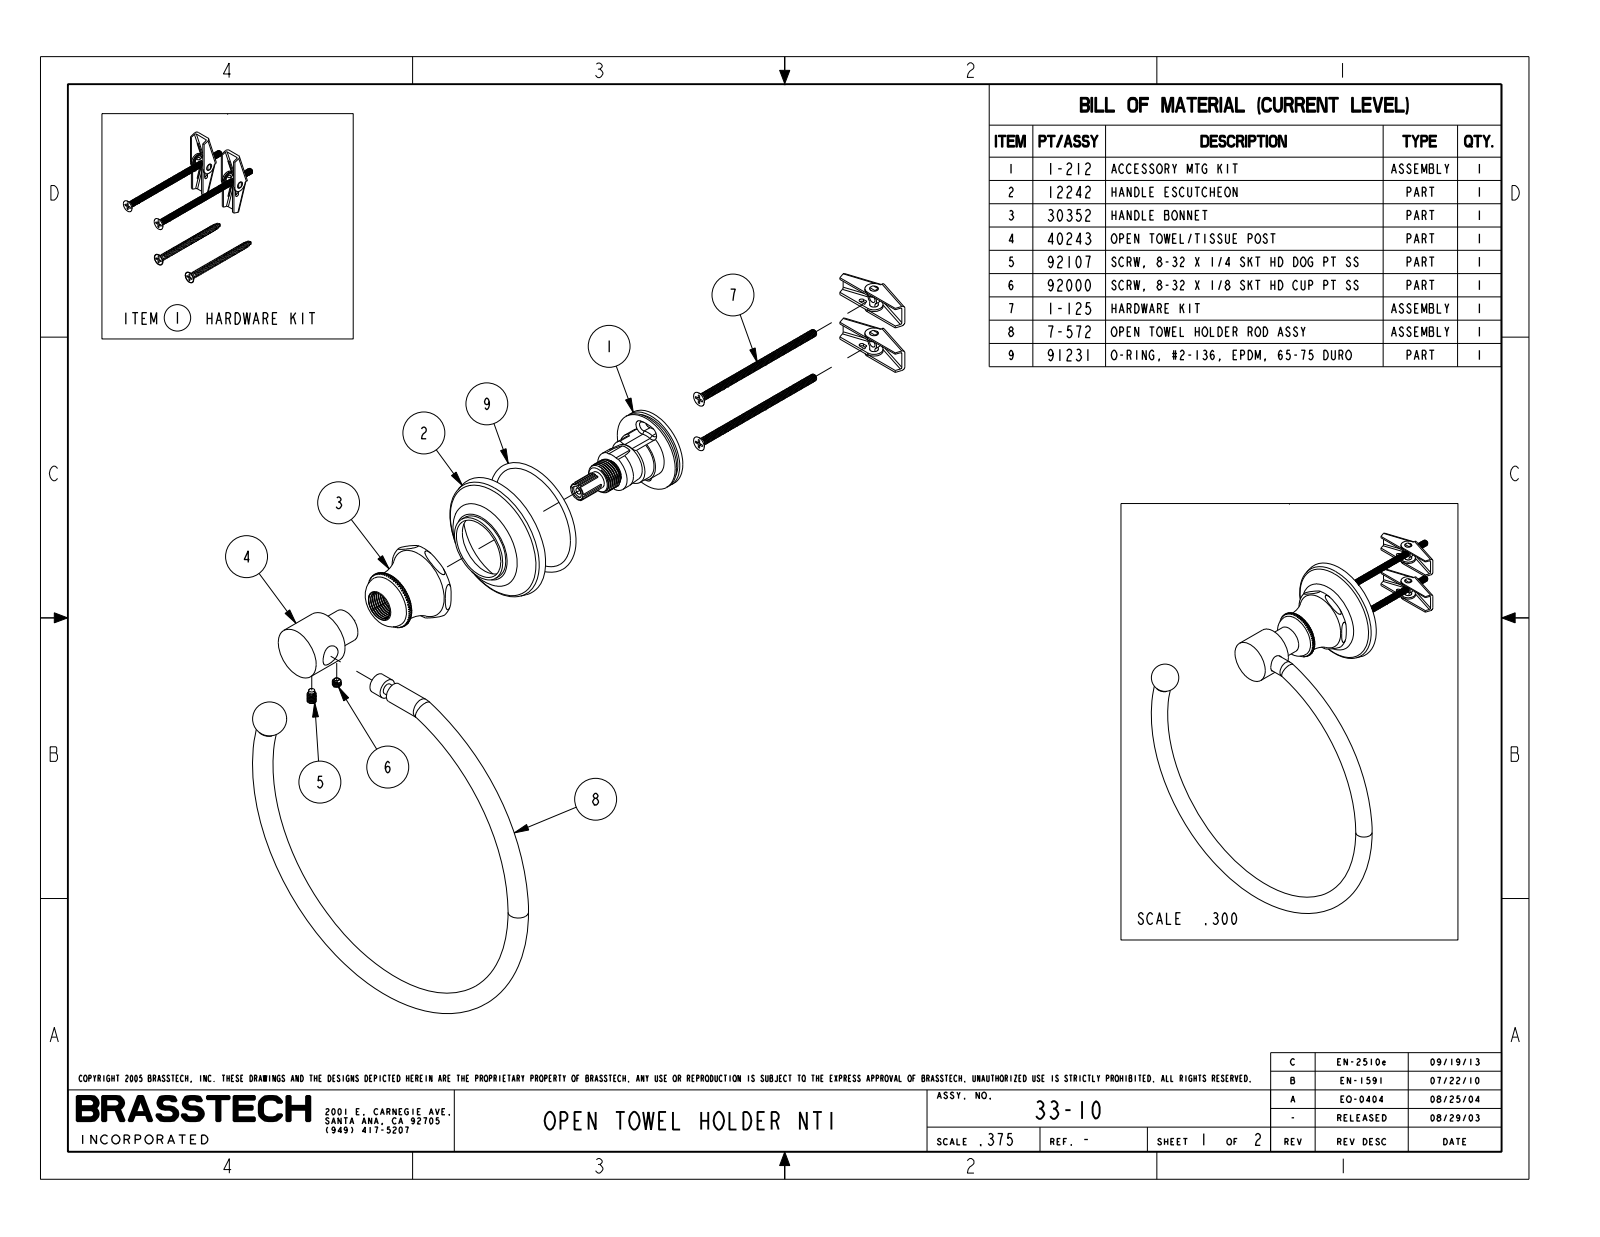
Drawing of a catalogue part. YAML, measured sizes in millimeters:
part_name: "33-10_WEB"
step_written_by: "PRO/ENGINEER BY PARAMETRIC TECHNOLOGY CORPORATION, 2009300 (CONFIG_CONTROL_DESIGN)"
units: millimeters
bodies: {solids: 0, faces: 79, planar: 36, cylindrical: 10, other: 33}
overall_size: [203.1, 177.8, 75.9]
round_bosses_or_shafts:
  - {diameter: 9.5, count: 2}
  - {diameter: 24.9, count: 1}
  - {diameter: 15.9, count: 1}
face_to_face_distances: [54.8, 35.1, 19.1]
